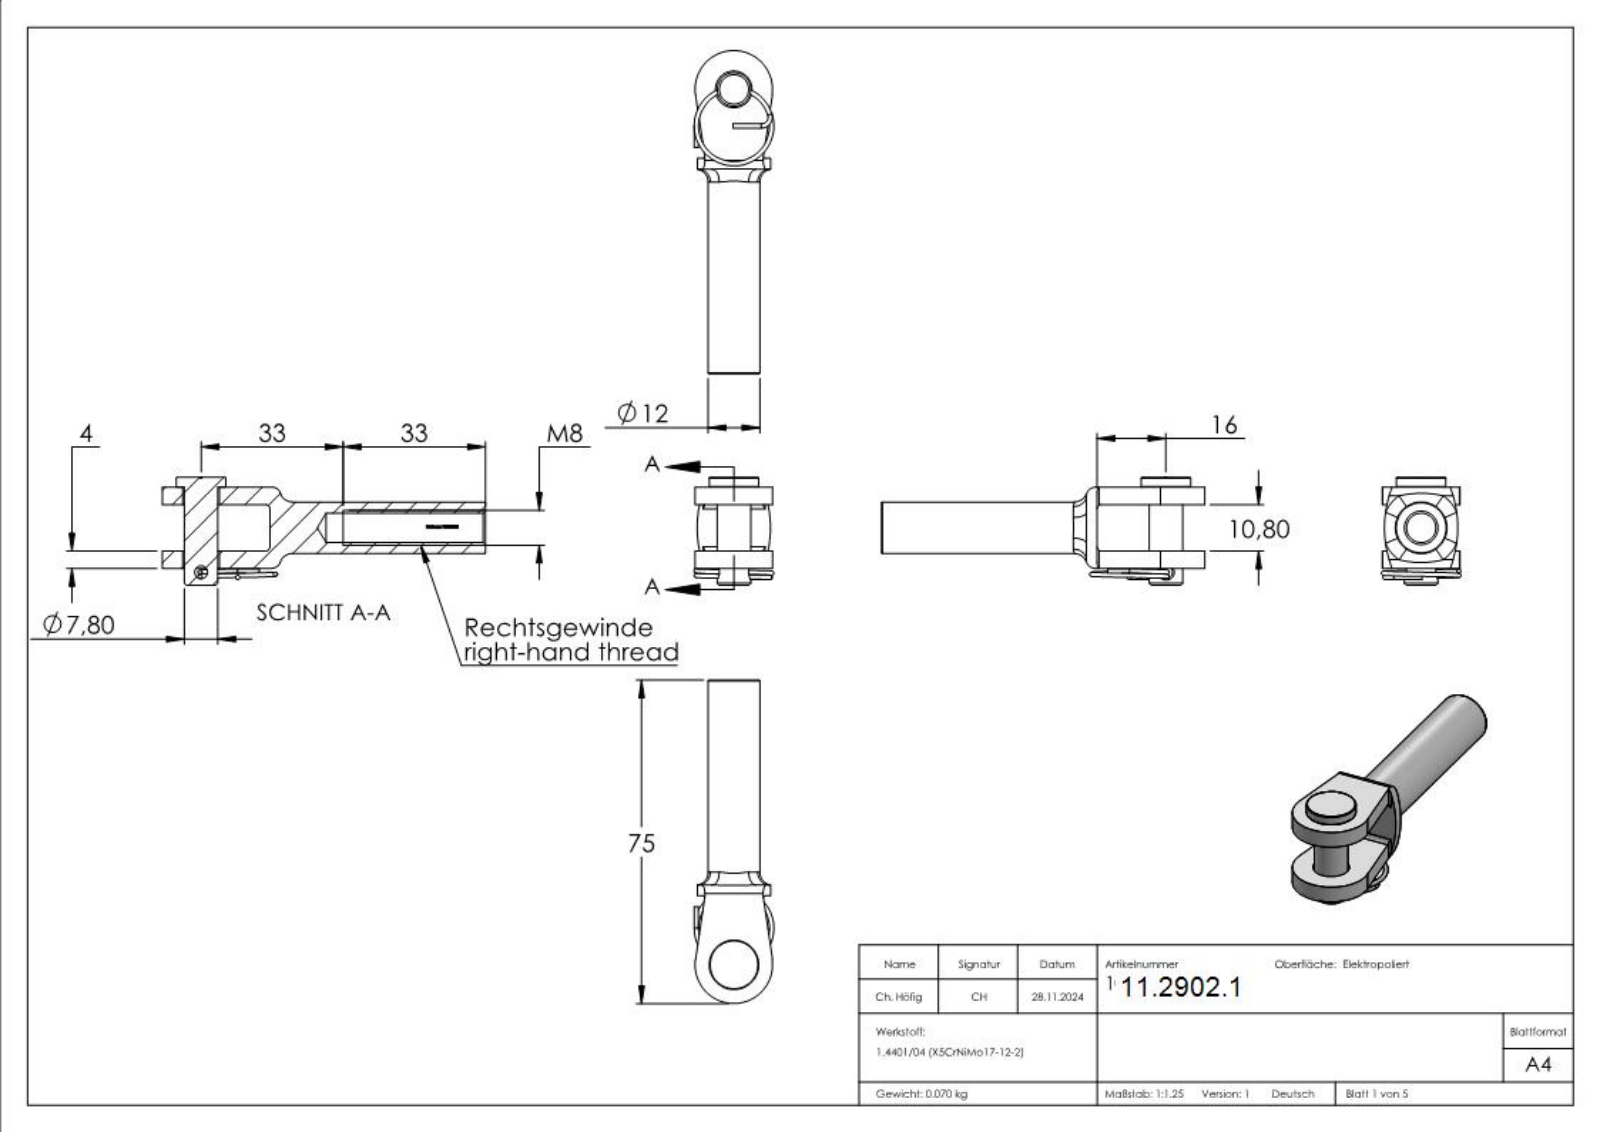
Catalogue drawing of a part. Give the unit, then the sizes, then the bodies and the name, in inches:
Units: inches
Overall size (bounding box): 2.953 × 0.984 × 0.728
Round holes (diameter × count): ⌀0.118 ×1, ⌀0.268 ×1, ⌀0.335 ×1
Round bosses / shafts (diameter × count): ⌀0.039 ×2, ⌀0.472 ×1, ⌀0.453 ×1, ⌀0.307 ×1
Partial cylindrical surfaces — rounded edges, fillets, slot ends (radius × count): R0.016 ×2, R0.039 ×2, R0.079 ×2, R1.028 ×2, R0.138 ×1, R0.354 ×1
Main face-to-face distances: 0.157, 0.583, 0.74, 0.425, 0.831, 0.673, 0.248, 0.091, 1.969, 0.154
Volume: 0.533 in³ · Surface area: 9.808 in²
Bodies: 3 solids, 285 faces (85 planar, 55 cylindrical, 145 other)
Part name (STEP PRODUCT): 100050008; 10005000X Teil1_100050008 Teil1; 10005000X Teil3_100050008 Teil3; 10005000X Teil2_100050008 Teil2
STEP written by: SolidWorks 2018 (CONFIG_CONTROL_DESIGN)
